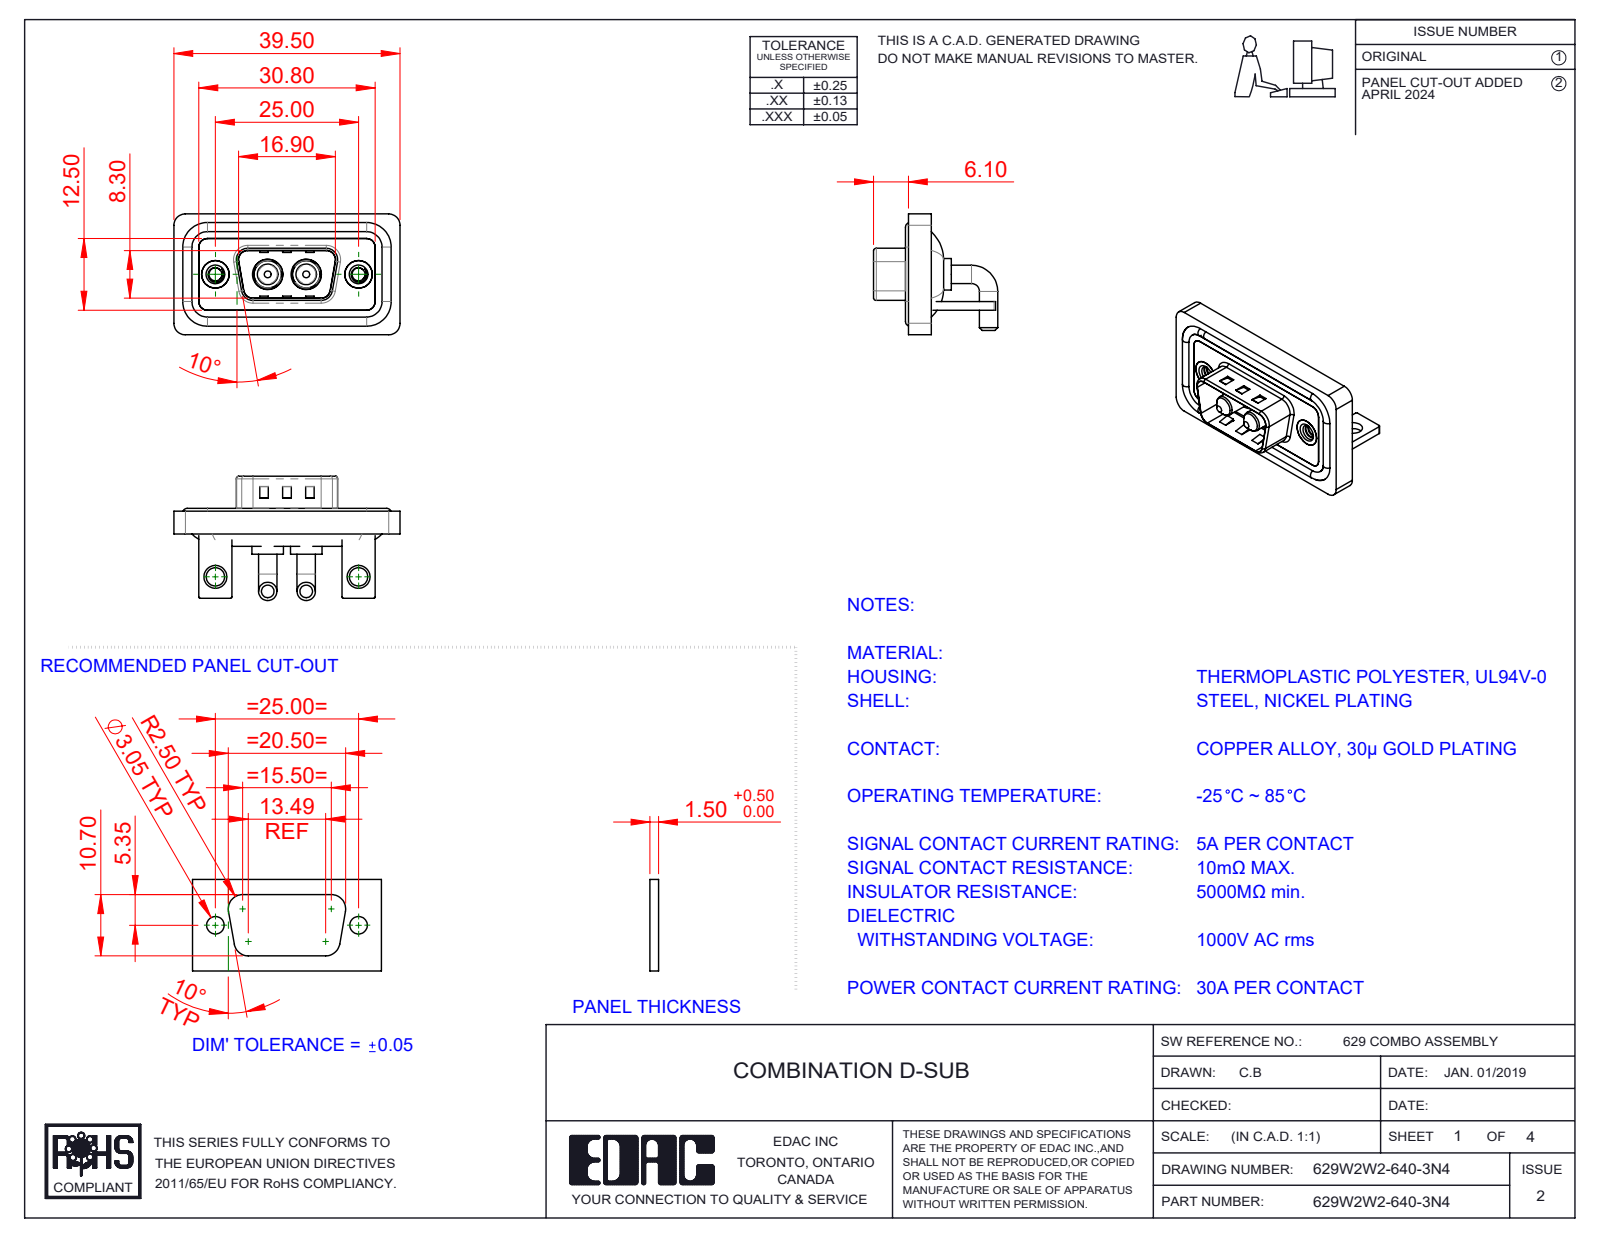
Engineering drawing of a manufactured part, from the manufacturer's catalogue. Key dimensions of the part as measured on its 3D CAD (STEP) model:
Part name (STEP PRODUCT): 629Combo Shell Rear_09 Contacts; 629Combo Housing_2W2; 629Combo Stabilizer Bracket; 629Combo Threaded Rivet_3 (+4 more)
STEP written by: SolidWorks 2023 (CONFIG_CONTROL_DESIGN)
Units: millimetres
Bodies: 13 solids, 537 faces (185 planar, 240 cylindrical, 112 other)
Overall size (bounding box): 39.5 × 21.7 × 21.1
Volume: 4 918 mm³ · Surface area: 7 791 mm²
Round holes (diameter × count): ⌀2.26 ×2, ⌀3.2 ×2, ⌀4 ×2, ⌀4.8 ×2, ⌀4.85 ×2, ⌀5 ×2, ⌀5.3 ×2
Round bosses / shafts (diameter × count): ⌀3.2 ×4, ⌀1.6 ×4, ⌀5.5 ×2, ⌀5.2 ×2, ⌀4.9 ×2, ⌀4.75 ×2, ⌀3.75 ×2, ⌀3.6 ×2
Partial cylindrical surfaces — rounded edges, fillets, slot ends (radius × count): R2 ×19, R1.5 ×18, R0.25 ×16, R0.5 ×9, R1.6 ×8, R0.6 ×4, R0.65 ×4, R0.9 ×4
Main face-to-face distances: 0.4, 1.5, 2.9, 0.8, 1.1, 1.2, 2.1, 1.6, 3.7, 2.5
Hole centre spacings: 9.14, 15.86, 25, 6.72
